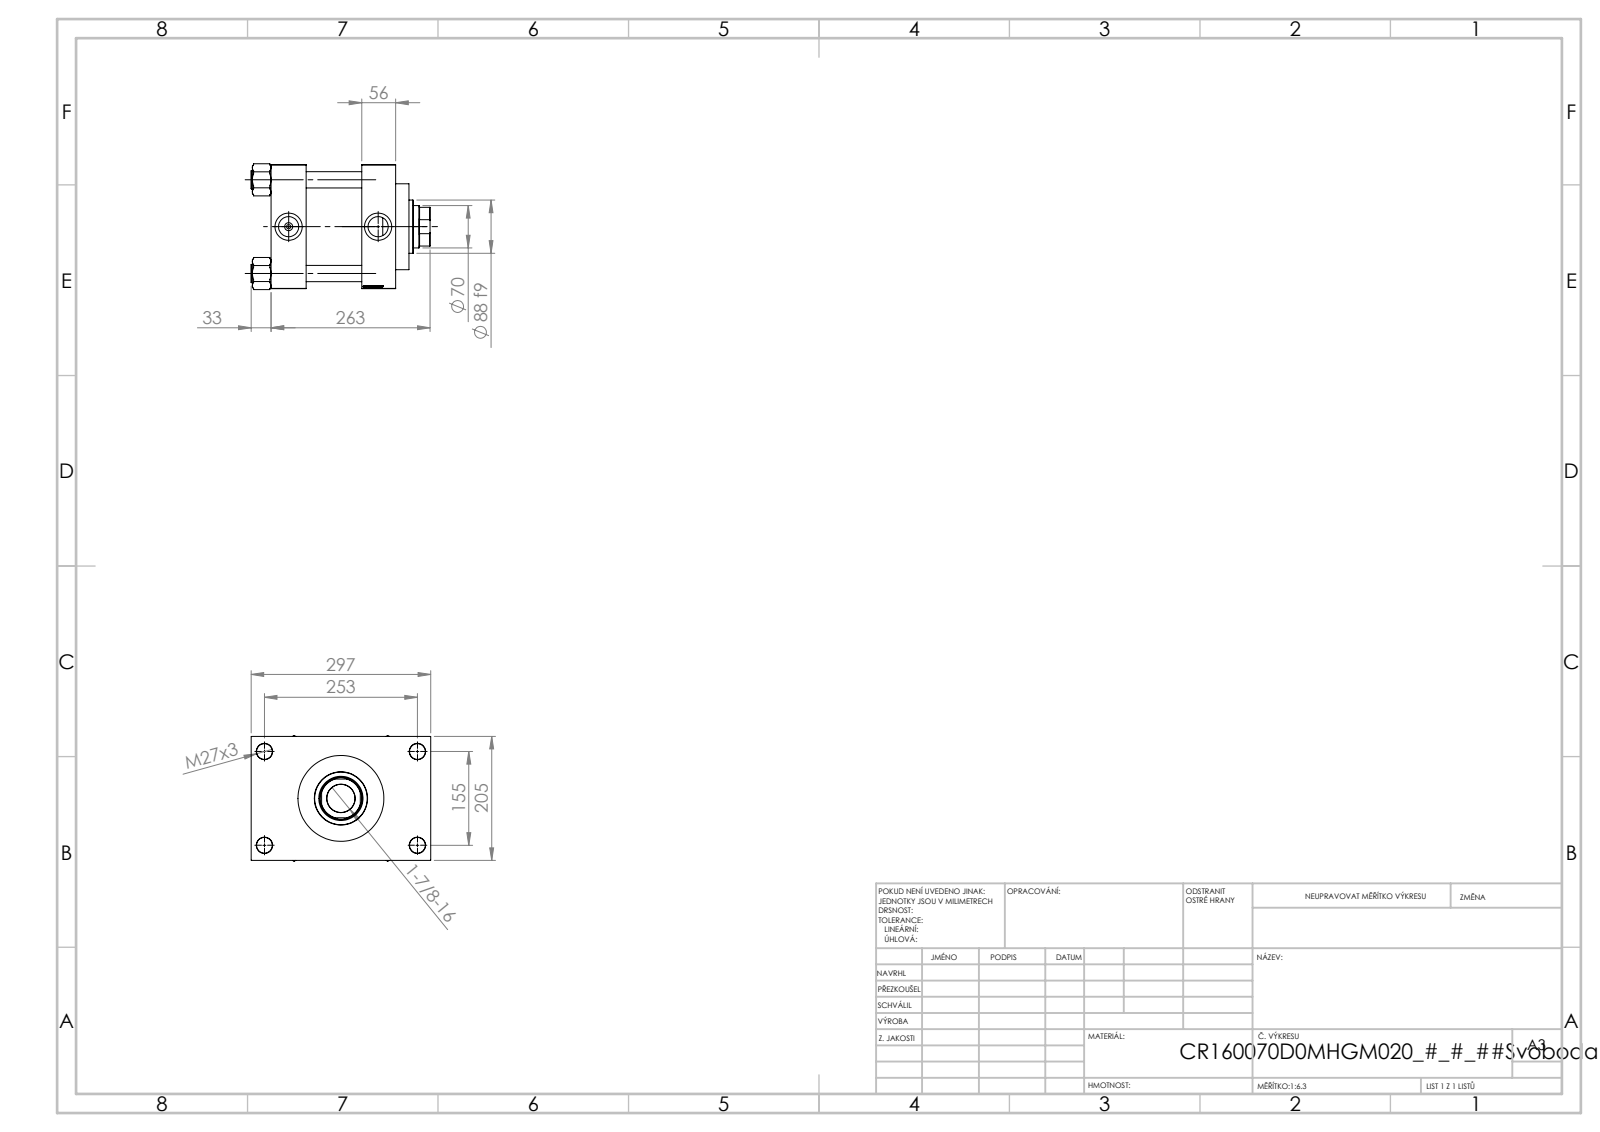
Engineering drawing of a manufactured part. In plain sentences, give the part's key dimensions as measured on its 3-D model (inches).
The part is named "NUT_M5_D; V215CR_VCP_D; V215CR_D_TYCINKA; V215_VC_A (+1 more)". Its 3-D file was written by "SolidWorks 2019 (CONFIG_CONTROL_DESIGN)". It is 11 solids with 1148 faces: 544 planar, 86 cylindrical and 518 other. Overall it measures 11.693 by 11.654 by 8.194 inches. Its volume is 479.4 cubic inches and its surface area 1 131 square inches. Round holes: 4 of diameter 1.024, 4 of diameter 1.063, 2 of diameter 0.276, 2 of diameter 1.309, 2 of diameter 1.772, 1 of diameter 1.831, 1 of diameter 2.756, 1 of diameter 2.874, 1 of diameter 4.724, 1 of diameter 5.591, 1 of diameter 6.299. Round bosses or shafts: 4 of diameter 1.181, 1 of diameter 6.535, 1 of diameter 3.465. Partial cylindrical surfaces (rounded edges, fillets, slot ends): 1 of radius 1.339. The main face-to-face distances are 2.283, 5.906, 3.622, 8.11, 5.827, 2.205, 8.071, 1.811, 9.882, 2.835. The hole center spacings are 1.931, 4.312, 5.841, 6.098, 6.399, 8.03, 10.084, 6.102.
